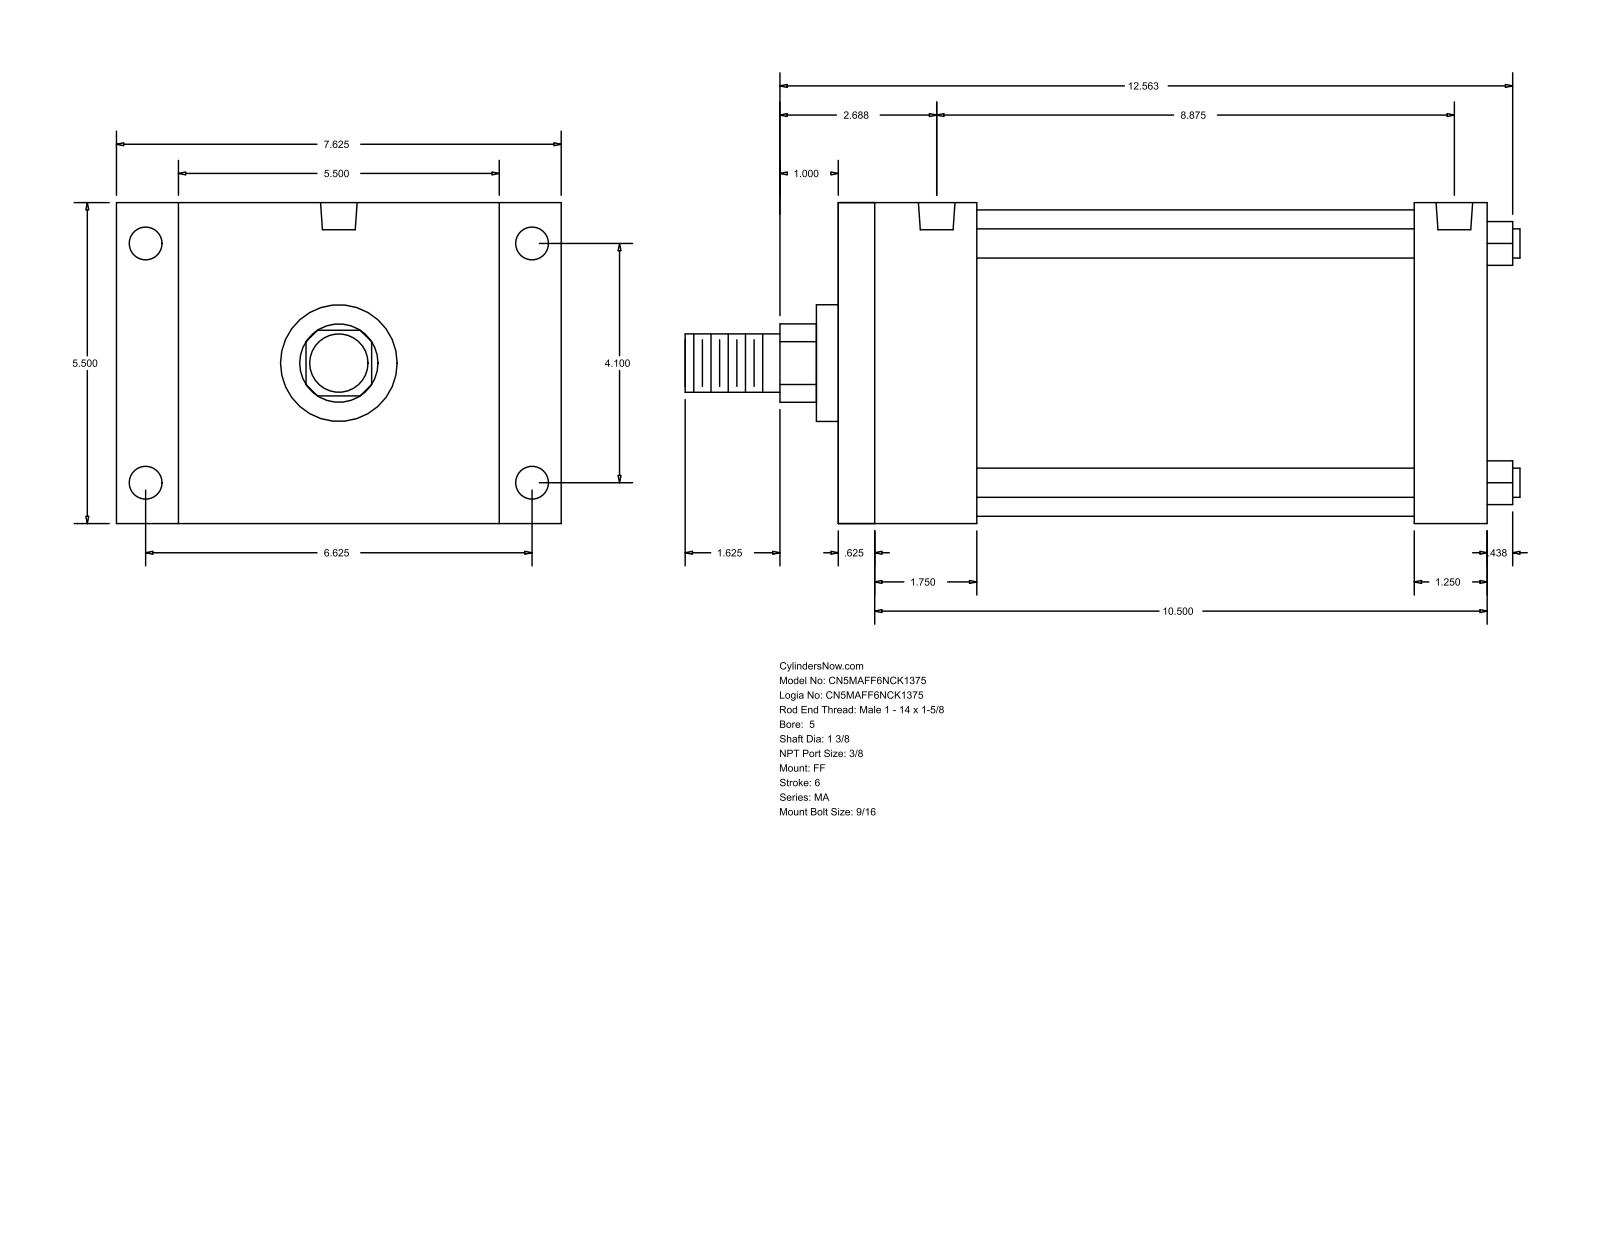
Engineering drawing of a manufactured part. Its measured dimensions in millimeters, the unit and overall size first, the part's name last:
Units: millimetres
Overall size (bounding box): 363.54 × 193.68 × 139.7
Round holes (diameter × count): ⌀11.11 ×4, ⌀14.29 ×4, ⌀15.93 ×2
Round bosses / shafts (diameter × count): ⌀12.7 ×4, ⌀133.35 ×1, ⌀50.8 ×1, ⌀34.92 ×1, ⌀25.4 ×1
Partial cylindrical surfaces — rounded edges, fillets, slot ends (radius × count): R17.06 ×1
Main face-to-face distances: 139.7, 282.58, 15.87, 266.71, 250.83, 234.96, 31.75, 60.32, 44.45, 190.51
Hole centre spacings: 104.14, 168.28, 197.9, 215.9, 4.76, 4.77, 220.66, 220.67
Bodies: 0 solids, 92 faces (64 planar, 28 cylindrical, 0 other)
Part name (STEP PRODUCT): MA_FF__0500_1.375
STEP written by: GSSL Pune (CONFIG_CONTROL_DESIGN)
